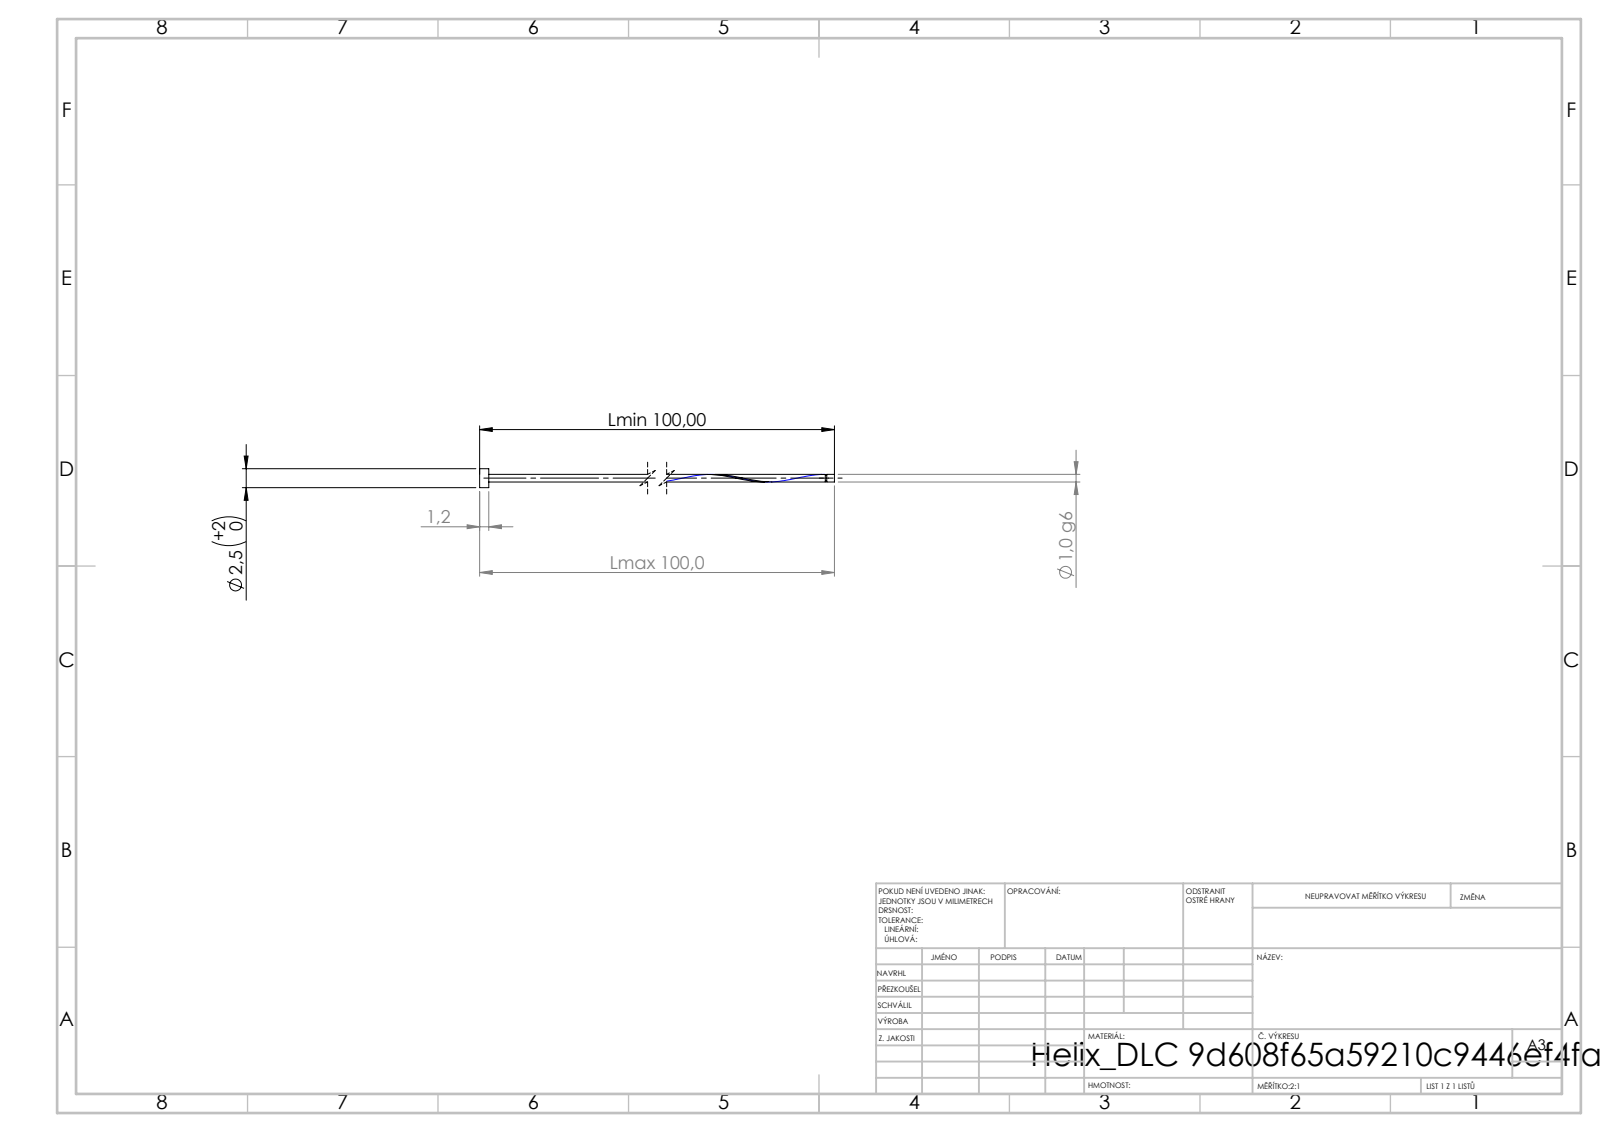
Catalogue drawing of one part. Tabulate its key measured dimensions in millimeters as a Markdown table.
| quantity | value |
| --- | --- |
| STEP written by | SolidWorks 2019 (CONFIG_CONTROL_DESIGN) |
| units | millimeters |
| bodies | 1 solid, 16 faces (6 planar, 9 cylindrical, 1 other) |
| overall size | 100 × 2.5 × 2.5 |
| volume | 98 mm³ |
| surface area | 429 mm² |
| round bosses / shafts (diameter × count) | 2.5 × 1, 1 × 1, 0.8 × 1 |
| main face-to-face distances | 1.2, 98.8, 100, 99, 97.8, 1, 97.6, 53.8, 52.6, 45 |
